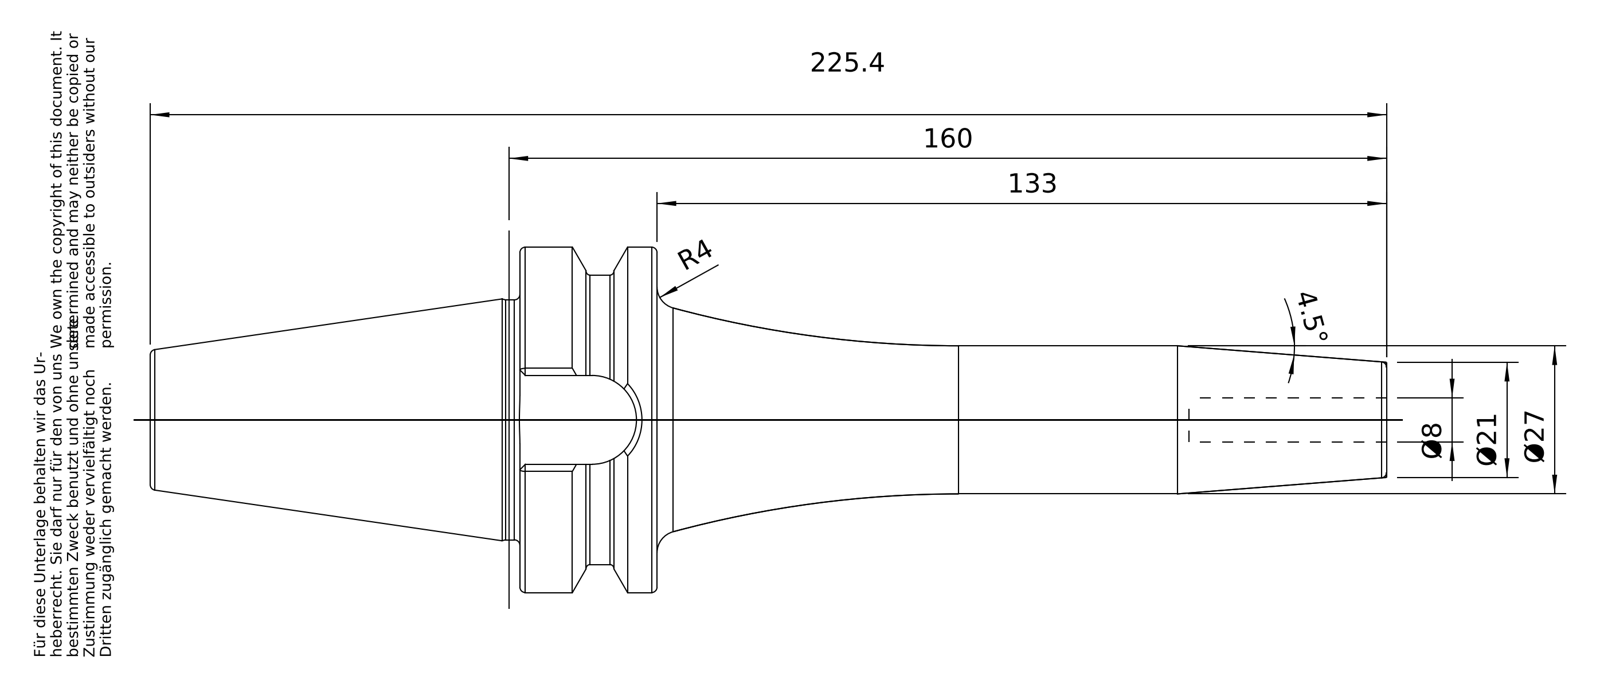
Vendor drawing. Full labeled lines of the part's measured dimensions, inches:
Part name (STEP PRODUCT): 40-642-08
STEP written by: PRO/ENGINEER BY PARAMETRIC TECHNOLOGY CORPORATION, 2010430 (CONFIG_CONTROL_DESIGN)
Units: inches
Bodies: 1 solid, 98 faces (26 planar, 22 cylindrical, 50 other)
Overall size (bounding box): 8.874 × 2.48 × 2.48
Volume: 12.82 in³ · Surface area: 51.81 in²
Round holes (diameter × count): ⌀0.315 ×1, ⌀0.545 ×1, ⌀0.67 ×1, ⌀0.689 ×1
Round bosses / shafts (diameter × count): ⌀2.48 ×1, ⌀2.077 ×1, ⌀1.722 ×1, ⌀1.063 ×1, ⌀0.63 ×1
Partial cylindrical surfaces — rounded edges, fillets, slot ends (radius × count): R0.319 ×1
Main face-to-face distances: 0.984, 1.768, 6.22, 5.236, 0.638, 2.654, 3.638, 8.874, 1.417, 7.457
